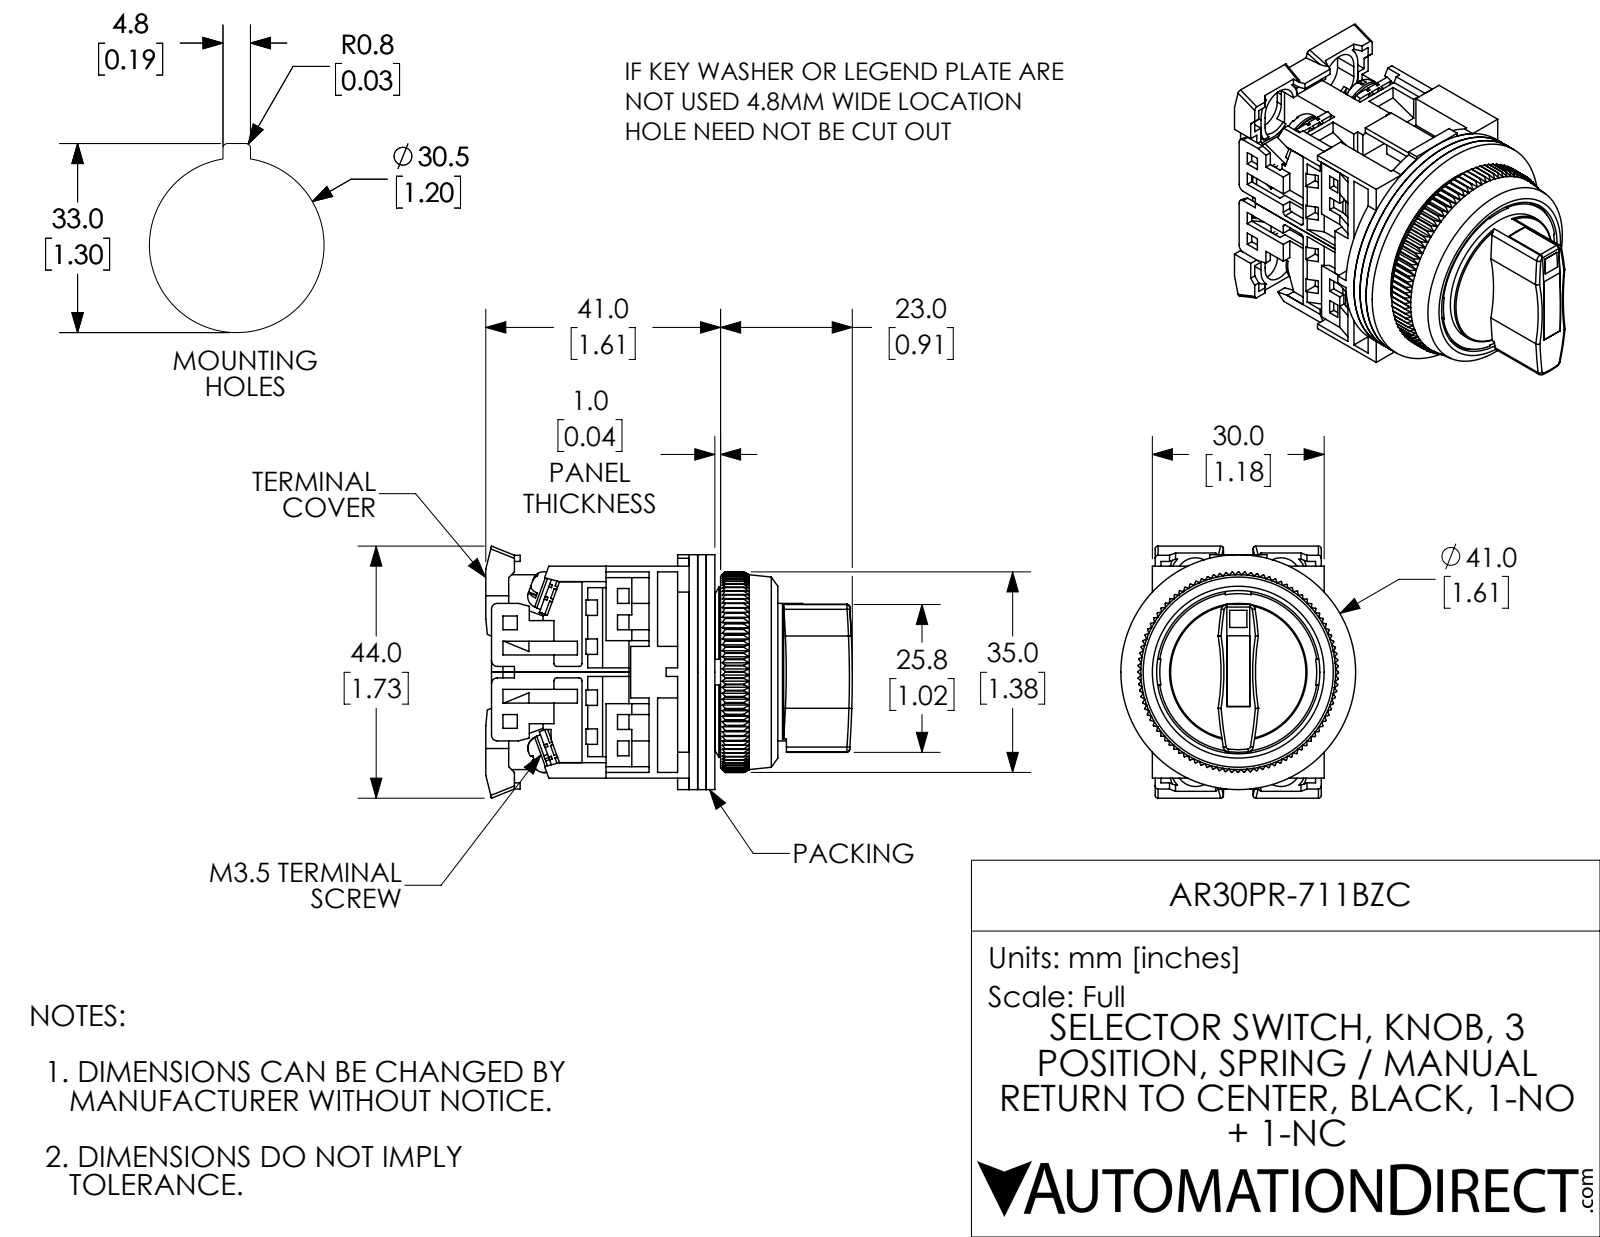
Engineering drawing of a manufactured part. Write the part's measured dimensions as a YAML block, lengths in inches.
part_name: "AR30PR-711BZC"
step_written_by: "SolidWorks 2017 (AUTOMOTIVE_DESIGN)"
units: inches
bodies: {solids: 26, faces: 1771, planar: 1219, cylindrical: 324, other: 228}
overall_size: [2.52, 1.732, 1.614]
volume: 2.318
surface_area: 62.54
round_holes:
  - {diameter: 0.138, count: 8}
  - {diameter: 0.142, count: 4}
  - {diameter: 0.118, count: 1}
  - {diameter: 0.315, count: 1}
  - {diameter: 0.472, count: 1}
  - {diameter: 0.48, count: 1}
  - {diameter: 0.512, count: 1}
  - {diameter: 0.819, count: 1}
  - {diameter: 0.945, count: 1}
  - {diameter: 1.122, count: 1}
  - {diameter: 1.252, count: 1}
round_bosses_or_shafts:
  - {diameter: 0.26, count: 4}
  - {diameter: 0.138, count: 4}
  - {diameter: 1.614, count: 1}
  - {diameter: 1.181, count: 1}
  - {diameter: 0.787, count: 1}
  - {diameter: 0.709, count: 1}
  - {diameter: 0.669, count: 1}
  - {diameter: 0.559, count: 1}
partial_cylinders:
  - {radius: 0.059, count: 16}
  - {radius: 0.02, count: 13}
  - {radius: 0.039, count: 8}
  - {radius: 0.138, count: 4}
  - {radius: 0.177, count: 4}
  - {radius: 0.118, count: 2}
  - {radius: 1.575, count: 2}
  - {radius: 1.638, count: 2}
face_to_face_distances: [0.059, 0.118, 0.039, 0.177, 1.417, 0.079, 1.358, 0.689, 0.091, 0.157]
hole_center_spacings: [0.579, 0.61]
